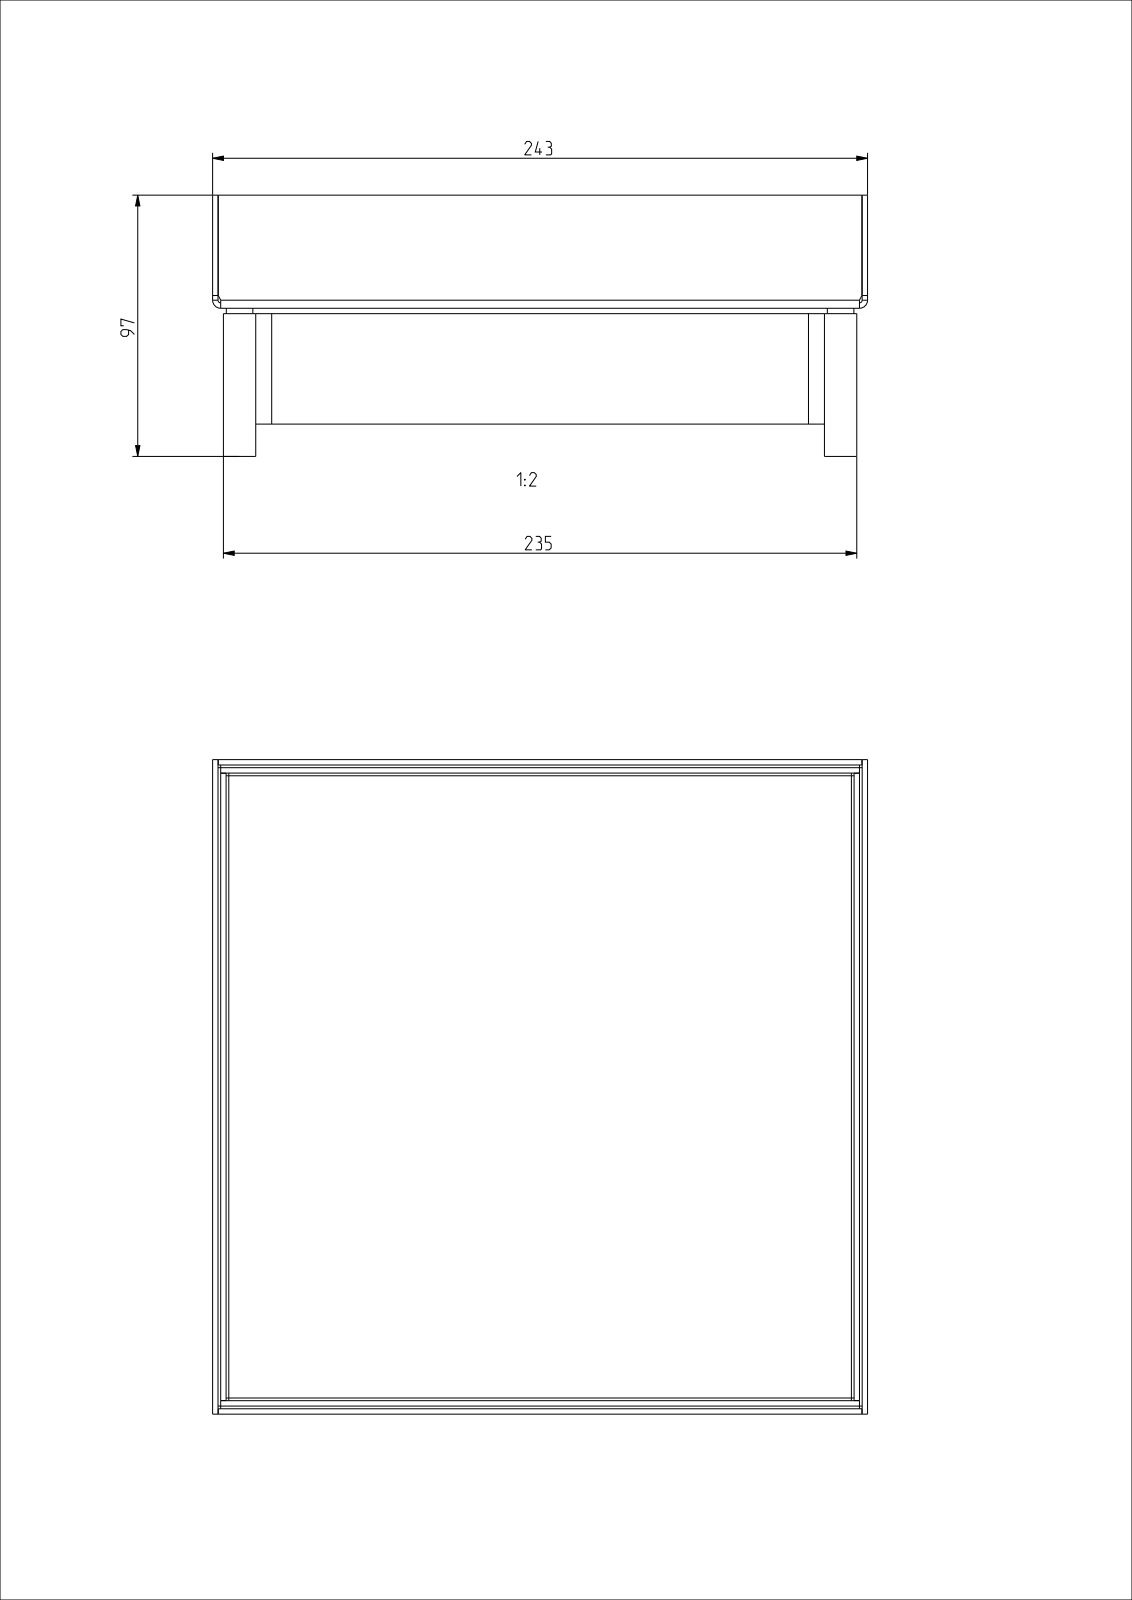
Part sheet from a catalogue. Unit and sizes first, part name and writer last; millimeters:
Units: millimetres
Overall size (bounding box): 243 × 243 × 97
Round holes (diameter × count): ⌀5 ×4, ⌀6.8 ×4, ⌀8.5 ×4, ⌀117 ×1
Round bosses / shafts (diameter × count): ⌀12 ×4, ⌀9.85 ×4
Partial cylindrical surfaces — rounded edges, fillets, slot ends (radius × count): R1 ×8, R3 ×8, R2 ×4, R150 ×1, R152.5 ×1
Main face-to-face distances: 2, 3, 235, 2.5, 238, 12, 10, 5, 234.5, 241
Hole centre spacings: 170.04, 63.64, 90, 94.05, 157.68, 221.32, 223, 127.28
Volume: 801 595 mm³ · Surface area: 451 640 mm²
Bodies: 8 solids, 186 faces (116 planar, 70 cylindrical, 0 other)
Part name (STEP PRODUCT): T-00631; T-00632; T-00625; T-00828_ASM (+4 more)
STEP written by: CREO PARAMETRIC BY PTC INC, 2022024 (AUTOMOTIVE_DESIGN)
